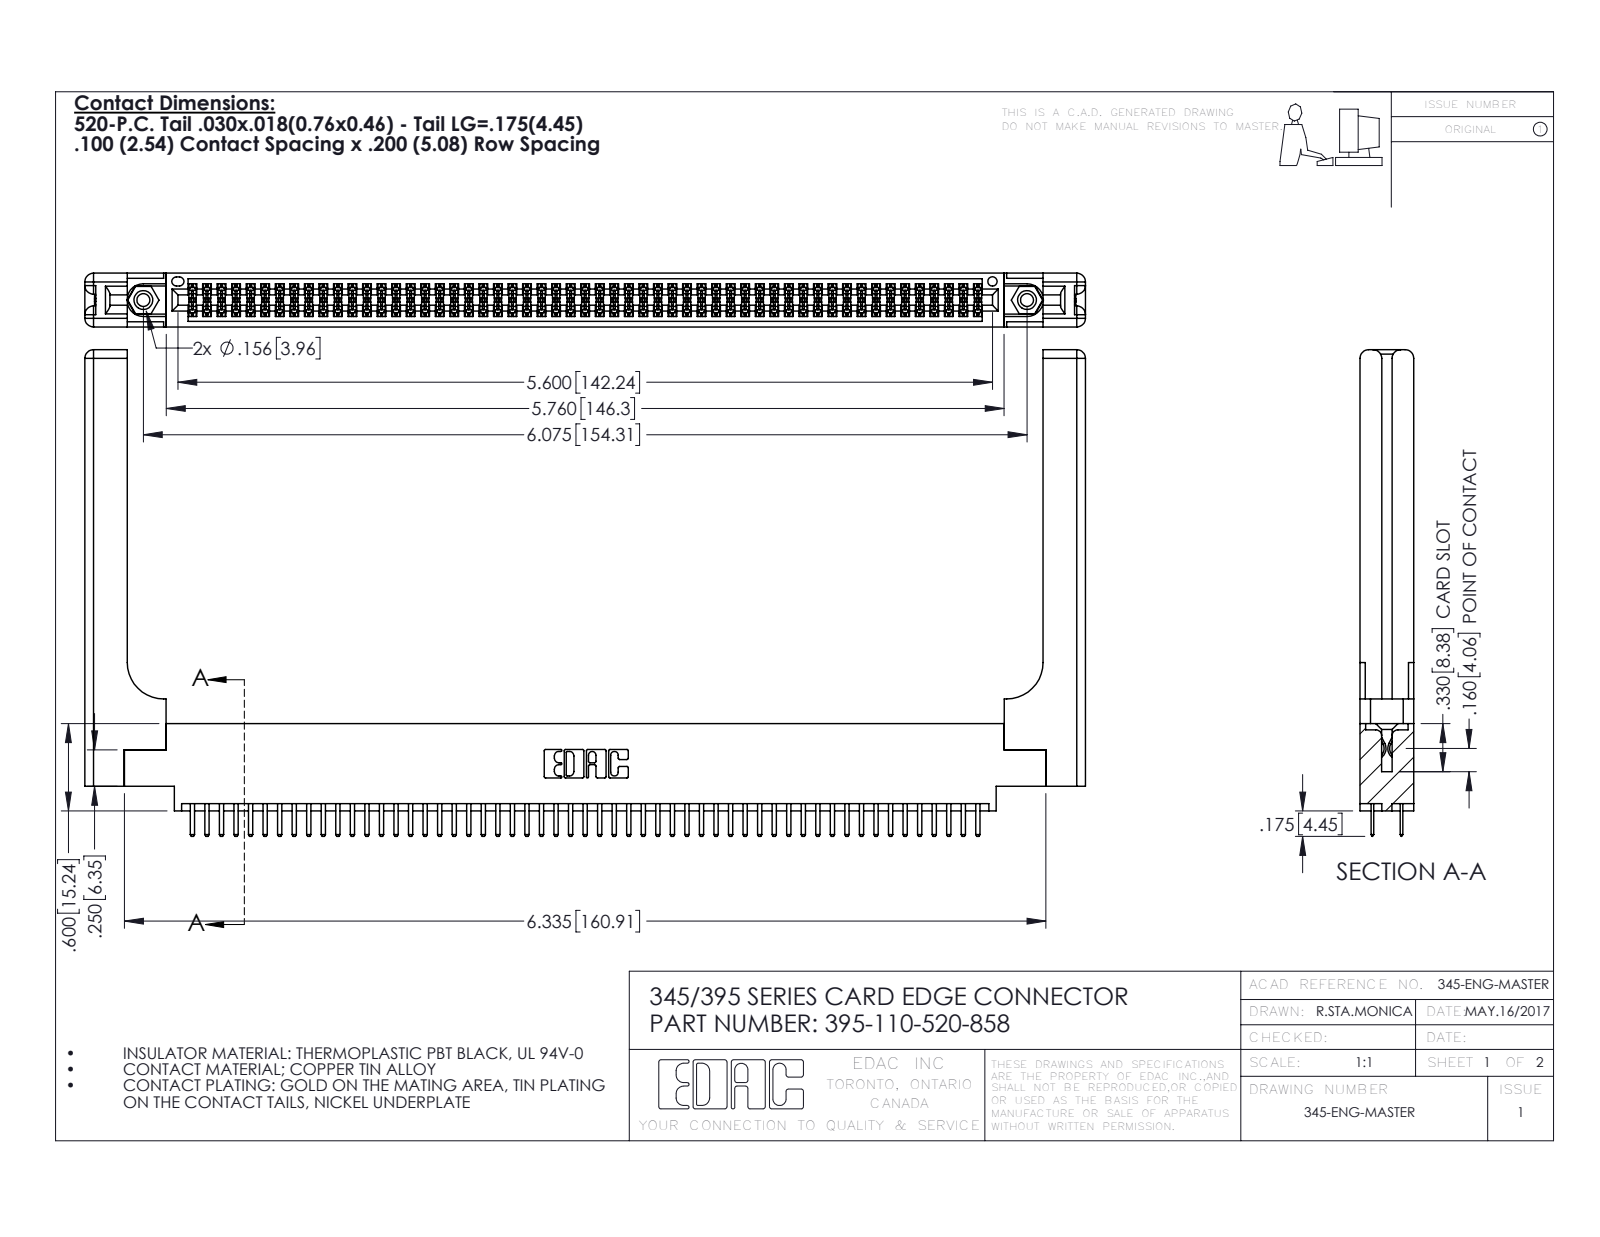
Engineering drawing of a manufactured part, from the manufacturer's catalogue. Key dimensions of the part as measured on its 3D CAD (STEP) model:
Part name (STEP PRODUCT): 345 Part_0.170 Offset - 0.156 Dia-TH; 345-220-058_345-220-058; 345-250-001_345-250-001-102; 345-292-001_345-293-120 (+1 more)
STEP written by: SolidWorks 2016 (CONFIG_CONTROL_DESIGN)
Units: inches
Bodies: 115 solids, 6326 faces (4082 planar, 2184 cylindrical, 60 other)
Overall size (bounding box): 6.879 × 3.345 × 0.37
Volume: 1.55 in³ · Surface area: 47.09 in²
Round holes (diameter × count): ⌀0.089 ×2, ⌀0.125 ×2, ⌀0.156 ×2, ⌀0.064 ×1
Round bosses / shafts (diameter × count): ⌀0.155 ×2
Partial cylindrical surfaces — rounded edges, fillets, slot ends (radius × count): R0.006 ×165, R0.01 ×114, R0.01 ×22, R0.06 ×16, R0.007 ×6, R0.031 ×6, R0.026 ×3, R0.014 ×2
Main face-to-face distances: 0.072, 0.37, 0.298, 0.2, 0.098, 0.272, 0.025, 0.225, 0.022, 0.175
Hole centre spacings: 0.27, 5.839, 6.075
